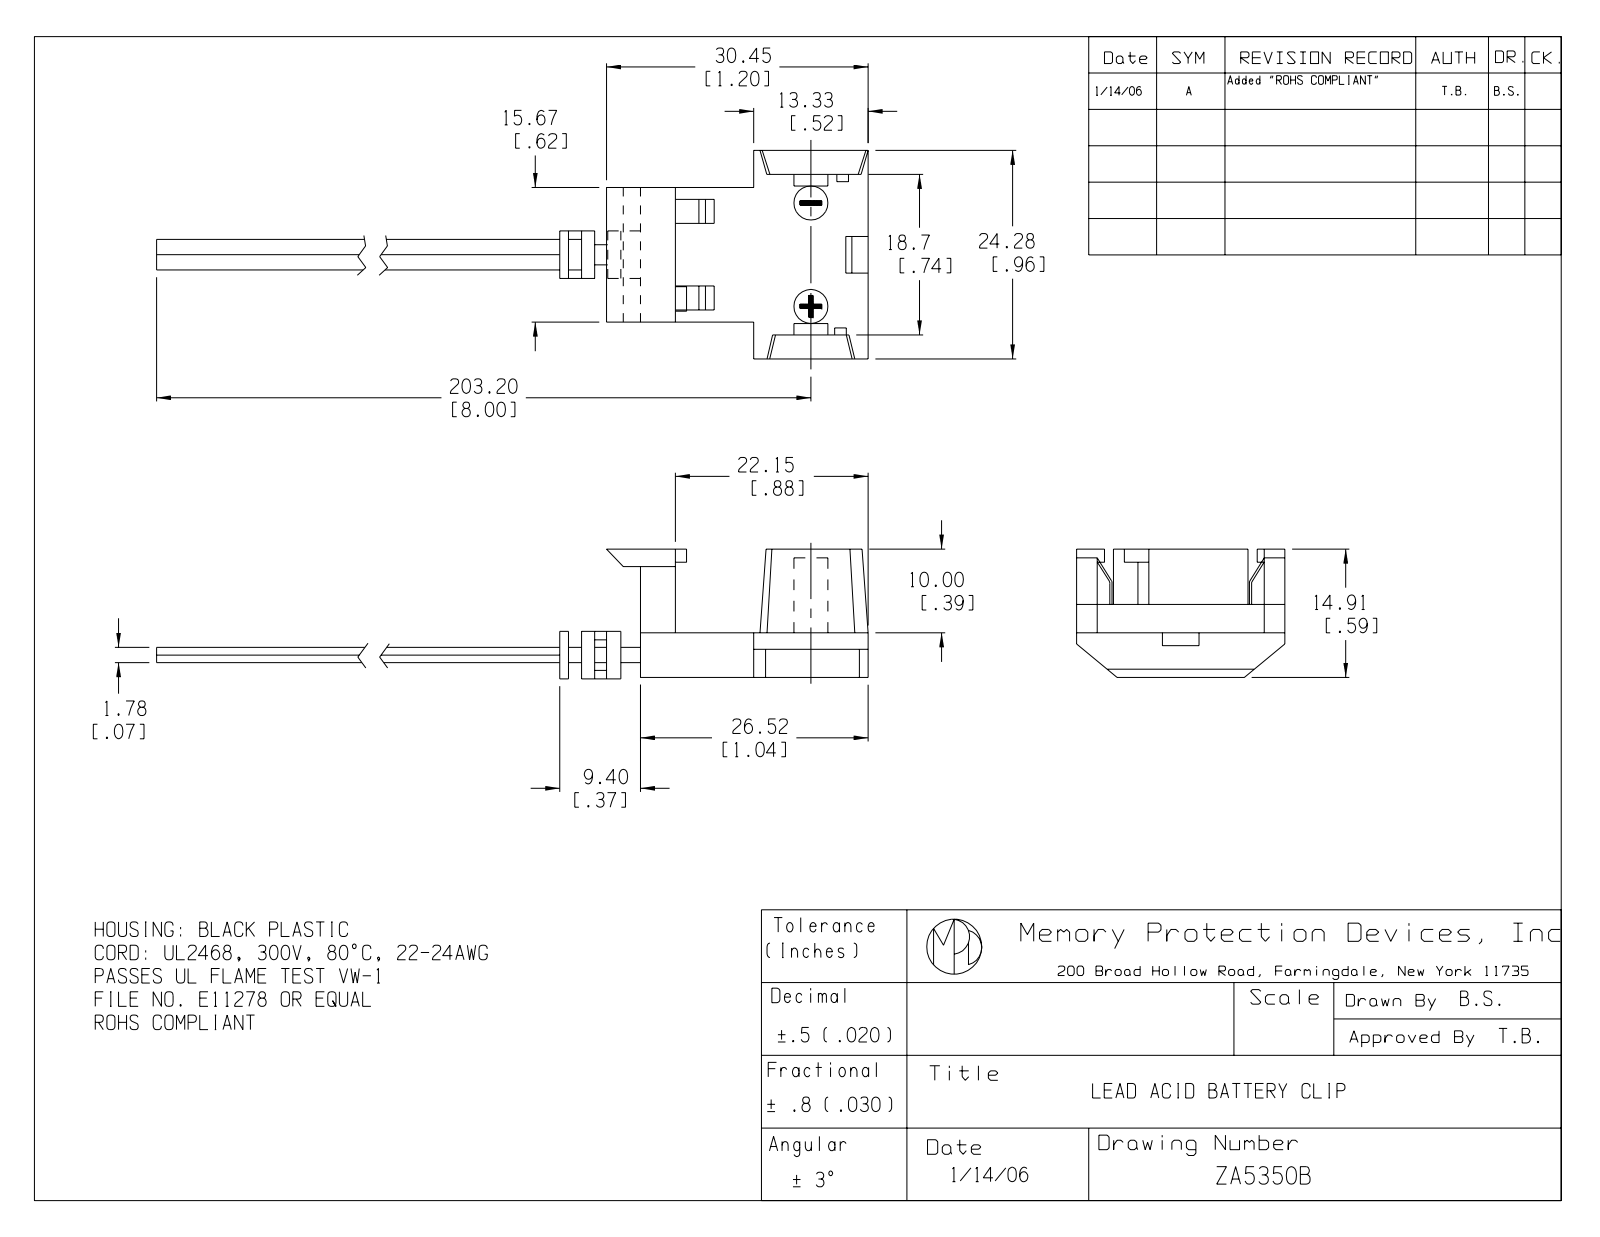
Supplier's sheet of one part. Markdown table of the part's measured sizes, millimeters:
| quantity | value |
| --- | --- |
| part name | ZA5350B |
| STEP written by | SolidWorks 2017 (AUTOMOTIVE_DESIGN) |
| units | millimeters |
| bodies | 5 solids, 151 faces (126 planar, 25 cylindrical, 0 other) |
| overall size | 209.87 × 24.28 × 14.91 |
| volume | 4 970 mm³ |
| surface area | 5 112 mm² |
| round holes (diameter × count) | 3.48 × 2 |
| round bosses / shafts (diameter × count) | 2 × 2, 4.5 × 1, 2.9 × 1 |
| partial cylindrical surfaces (radius × count) | 0.23 × 4 |
| main face-to-face distances | 4.92, 2.79, 4.3, 19.98, 21.49, 17.19, 1.51, 14.92, 10, 4.37 |
| hole center spacings | 12.46 |
